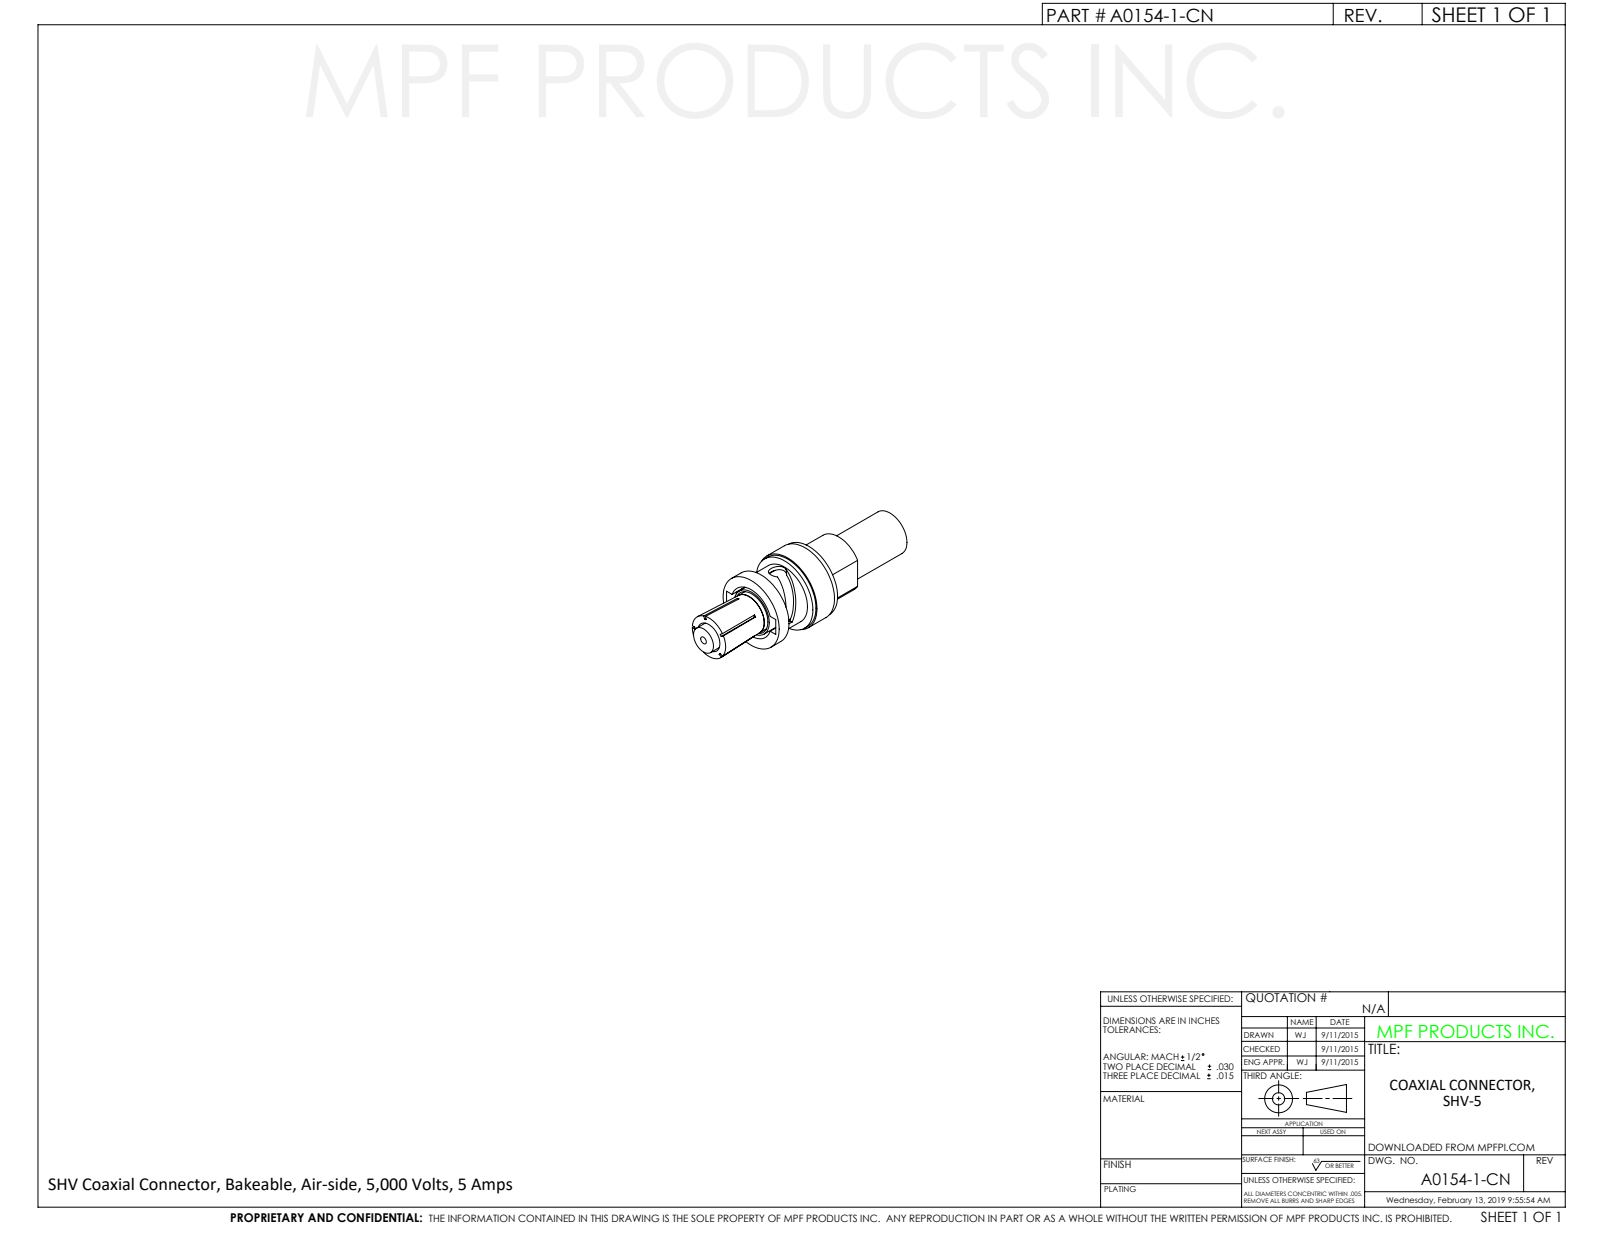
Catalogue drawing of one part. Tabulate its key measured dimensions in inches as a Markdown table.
| quantity | value |
| --- | --- |
| part name | A0154-1-CN |
| STEP written by | SolidWorks 2012 (CONFIG_CONTROL_DESIGN) |
| units | inches |
| bodies | 5 solids, 111 faces (65 planar, 38 cylindrical, 8 other) |
| overall size | 1.813 × 0.57 × 0.57 |
| volume | 0.187 in³ |
| surface area | 7.367 in² |
| round holes (diameter × count) | 0.054 × 1, 0.125 × 1, 0.155 × 1, 0.19 × 1, 0.315 × 1, 0.36 × 1, 0.39 × 1 |
| round bosses / shafts (diameter × count) | 0.57 × 1, 0.56 × 1, 0.55 × 1, 0.545 × 1, 0.445 × 1, 0.342 × 1, 0.33 × 1, 0.295 × 1 |
| partial cylindrical surfaces (radius × count) | 0.215 × 1 |
| main face-to-face distances | 0.29, 0.525, 0.85, 0.56, 0.325, 0.5, 0.79, 1.35, 1.025, 0.235 |
